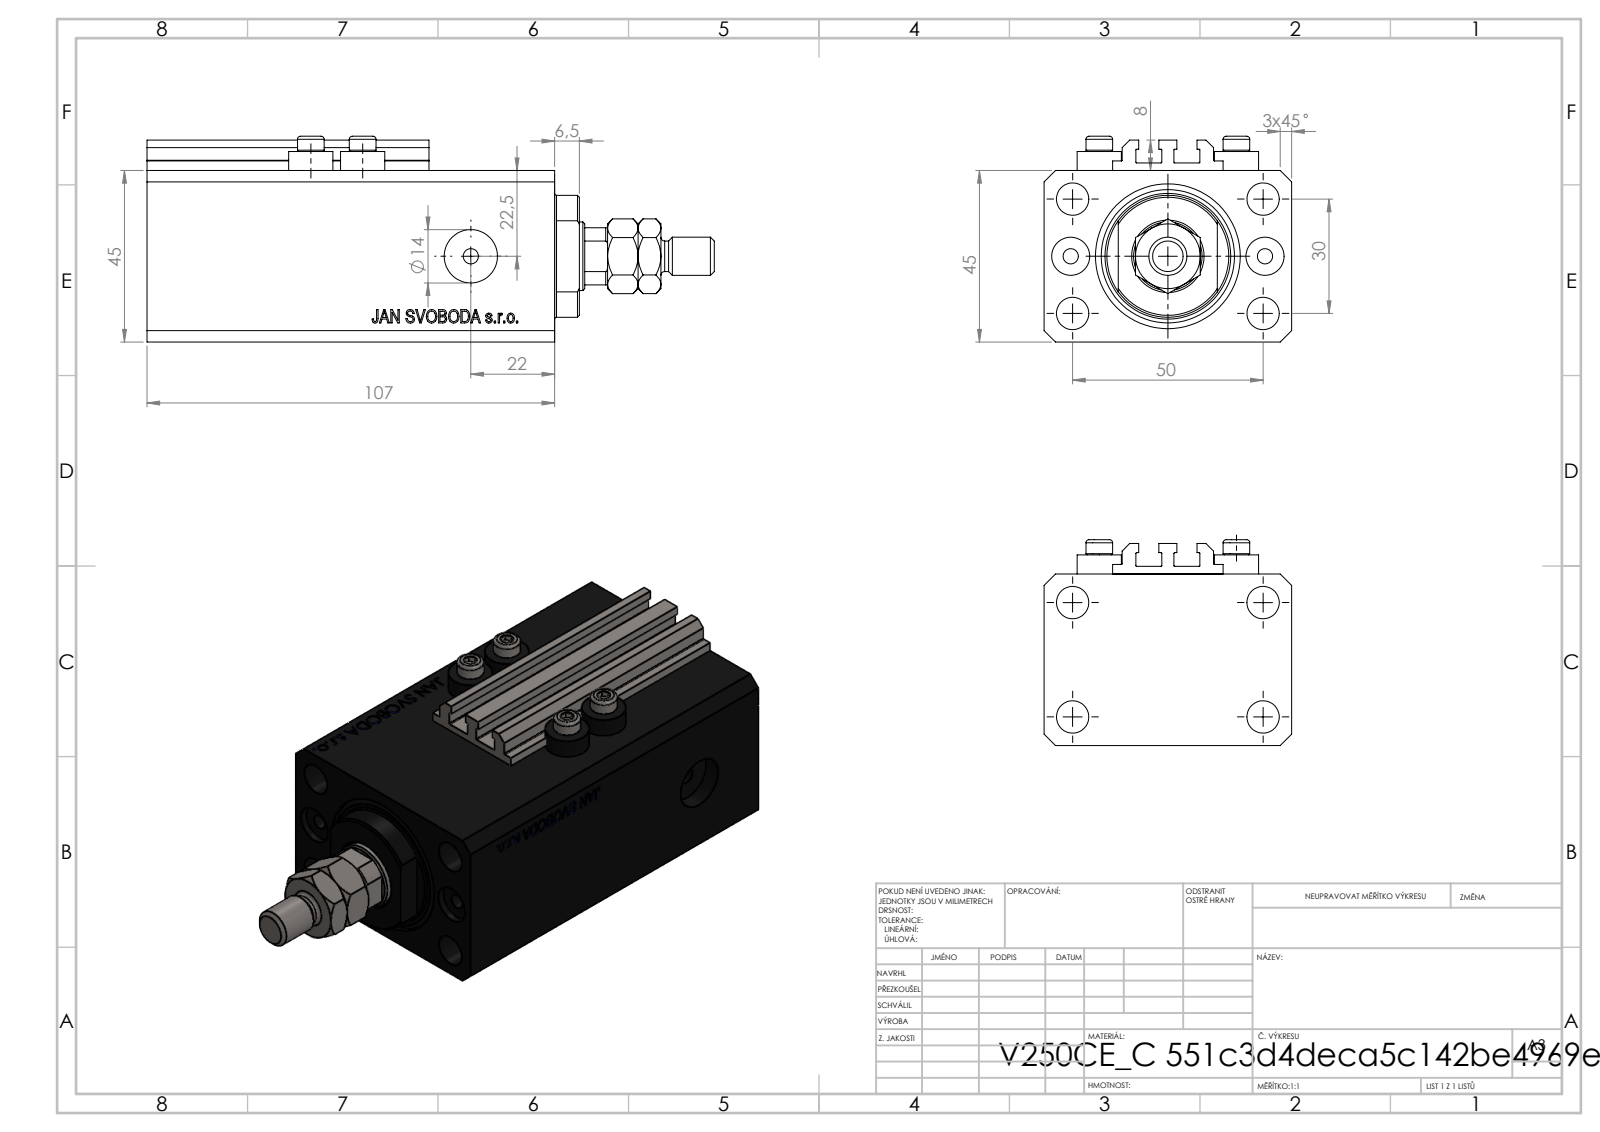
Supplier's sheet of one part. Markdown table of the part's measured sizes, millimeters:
| quantity | value |
| --- | --- |
| part name | V250CE_C_Body; V250CE_C_VCP; ALLEN BOLT V250CE; MTA (+1 more) |
| STEP written by | SolidWorks 2019 (CONFIG_CONTROL_DESIGN) |
| units | millimeters |
| bodies | 9 solids, 1082 faces (518 planar, 90 cylindrical, 474 other) |
| overall size | 148.9 × 65 × 54 |
| volume | 293 469 mm³ |
| surface area | 77 832 mm² |
| round holes (diameter × count) | 4 × 8, 8.5 × 5, 10 × 2, 14 × 2, 18 × 1, 25 × 1, 38 × 1 |
| round bosses / shafts (diameter × count) | 11.6 × 4, 7 × 4, 10 × 1, 8 × 1 |
| partial cylindrical surfaces (radius × count) | 0.2 × 10, 8.5 × 1, 16 × 1 |
| main face-to-face distances | 45, 65, 81.9, 107, 25.1, 47, 6.9, 2.5, 6, 10 |
| hole center spacings | 15.01, 29.15, 52.68, 13.6, 25.5, 30, 36, 38.48 |
